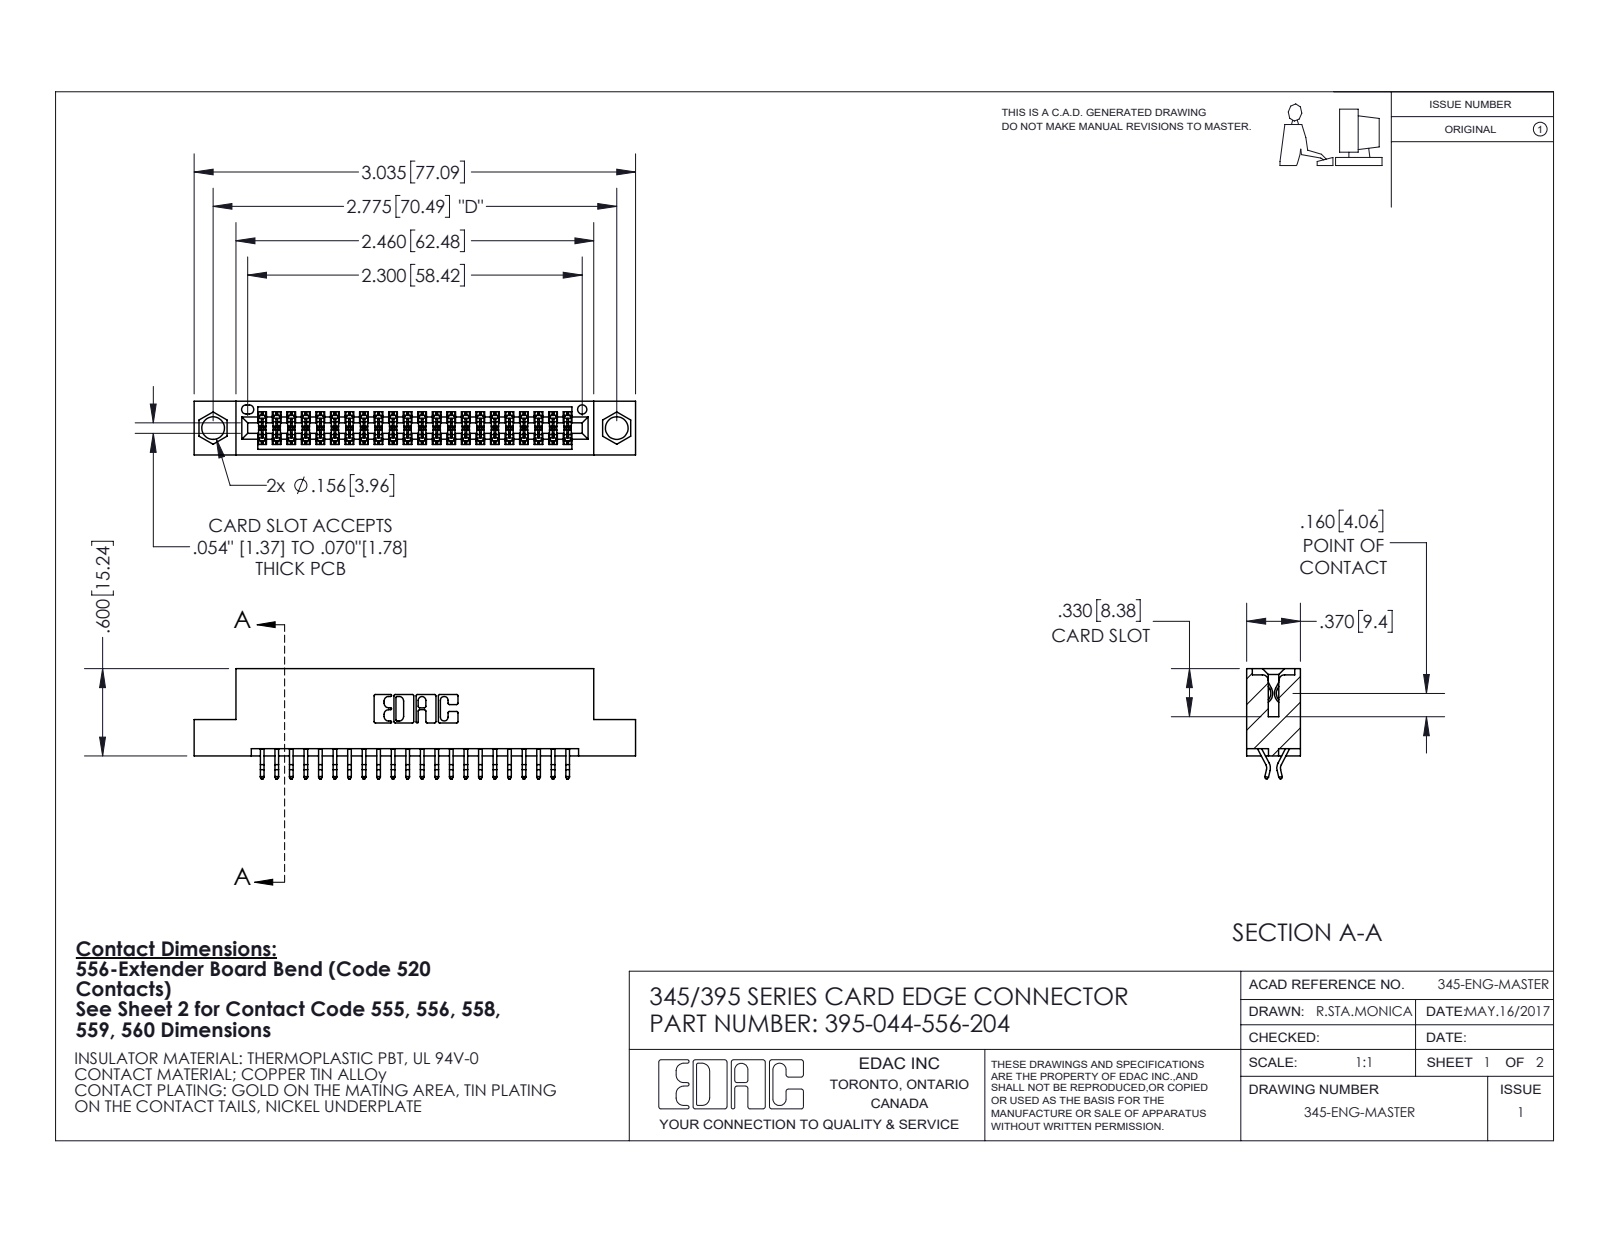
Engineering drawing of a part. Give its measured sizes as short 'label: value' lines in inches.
name: 345-292-001_556 Tail; 395-044-556-204; 345 Part_Flush Mounting Lugs - 0.156 Dia-TI
written by: SolidWorks 2020 (CONFIG_CONTROL_DESIGN)
unit: in
bodies: 45 solids, 2604 faces (1722 planar, 882 cylindrical, 0 other)
size: 3.035 × 0.757 × 0.37
volume: 0.439 in³; area: 15.6 in²
holes: 2× ⌀0.156, 1× ⌀0.064
rounds: 88× R0.006, 22× R0.01, 6× R0.007, 6× R0.031, 3× R0.026, 2× R0.01, 2× R0.014, 2× R0.019
face distances: 0.298, 0.072, 0.2, 0.37, 0.025, 0.098, 0.272, 0.225, 0.175, 0.149
hole spacings: 0.27, 2.541, 2.775
